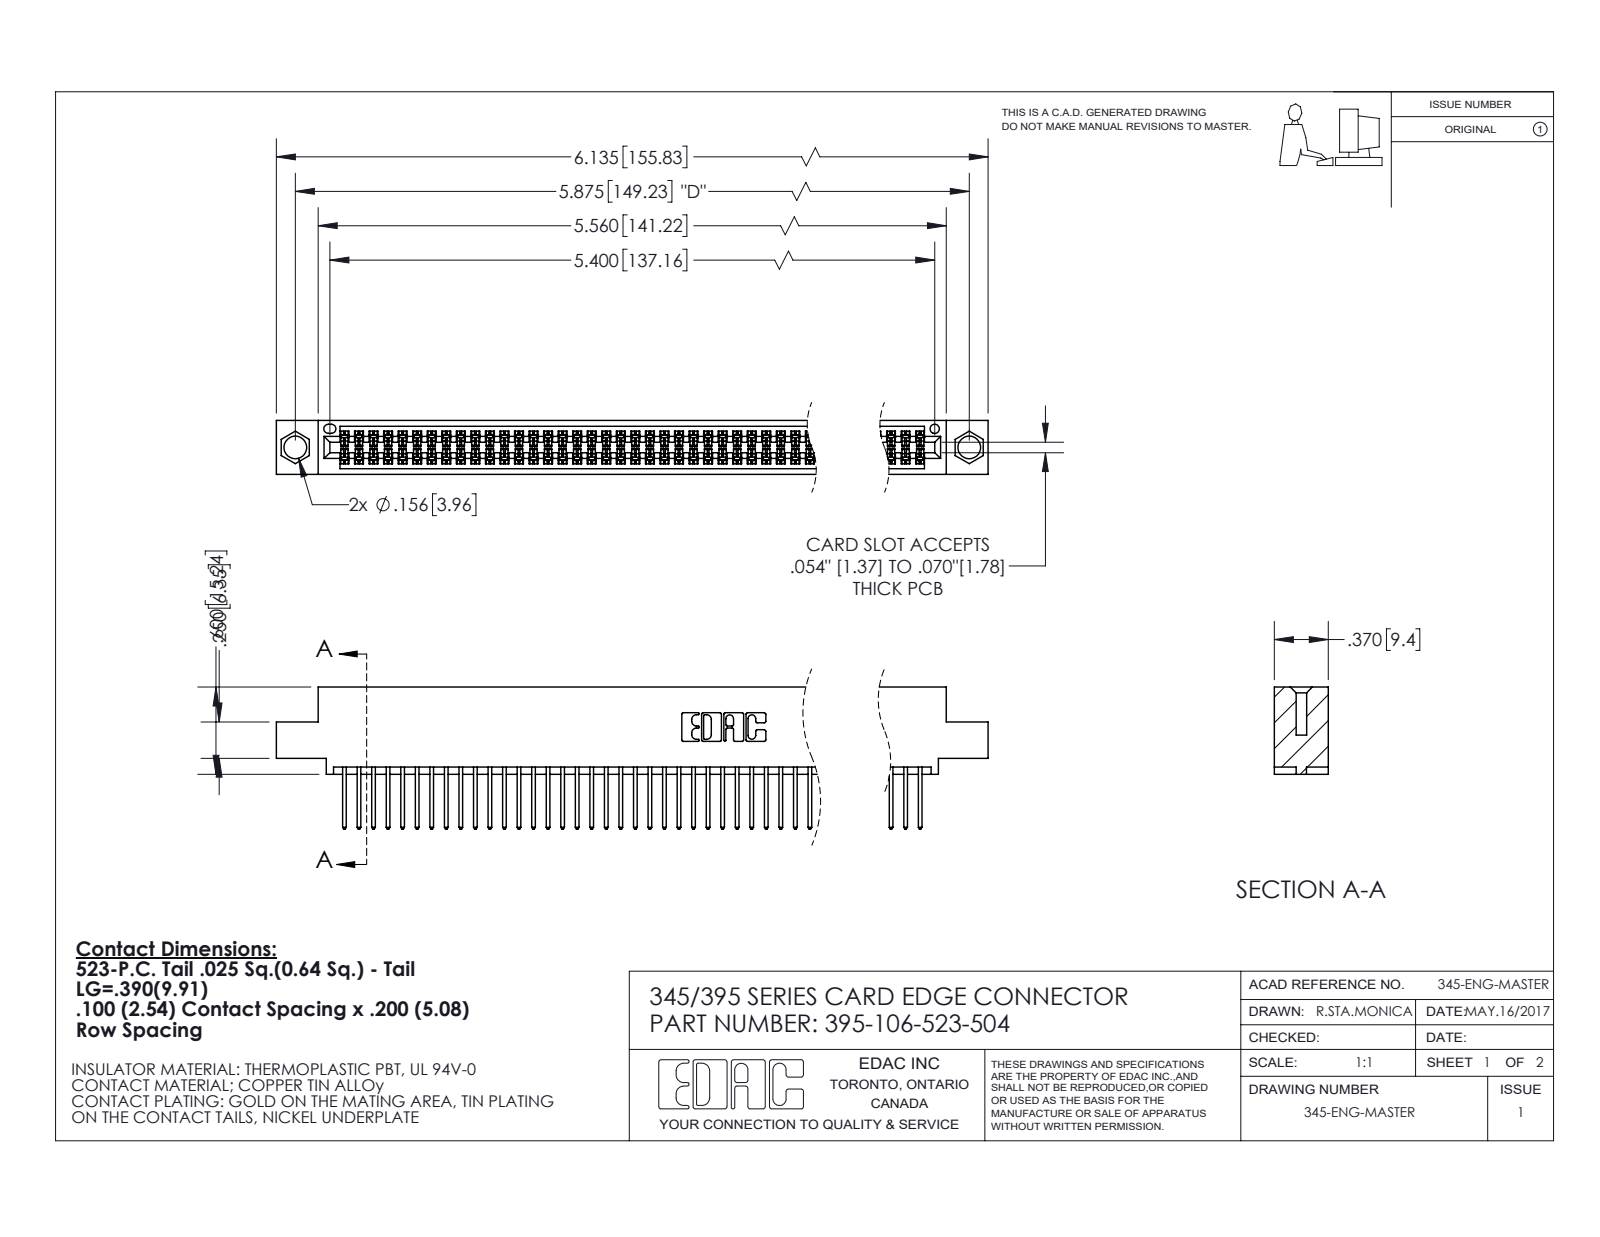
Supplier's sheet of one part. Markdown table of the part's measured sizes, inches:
| quantity | value |
| --- | --- |
| part name | 395-106-523-504; 345 Part_0.110 Offset - 0.156 Dia-TI; 345-292-001_345-293-123 |
| STEP written by | SolidWorks 2020 (CONFIG_CONTROL_DESIGN) |
| units | inches |
| bodies | 107 solids, 5444 faces (3596 planar, 1848 cylindrical, 0 other) |
| overall size | 6.135 × 0.977 × 0.37 |
| volume | 0.932 in³ |
| surface area | 36.76 in² |
| round holes (diameter × count) | 0.156 × 2, 0.064 × 1 |
| partial cylindrical surfaces (radius × count) | 0.006 × 159, 0.01 × 106, 0.01 × 22, 0.007 × 6, 0.031 × 6, 0.026 × 3, 0.014 × 2, 0.019 × 2 |
| main face-to-face distances | 0.298, 0.072, 0.2, 0.098, 0.272, 0.025, 0.37, 0.225, 0.175, 0.149 |
| hole center spacings | 0.27, 5.639, 5.875 |
